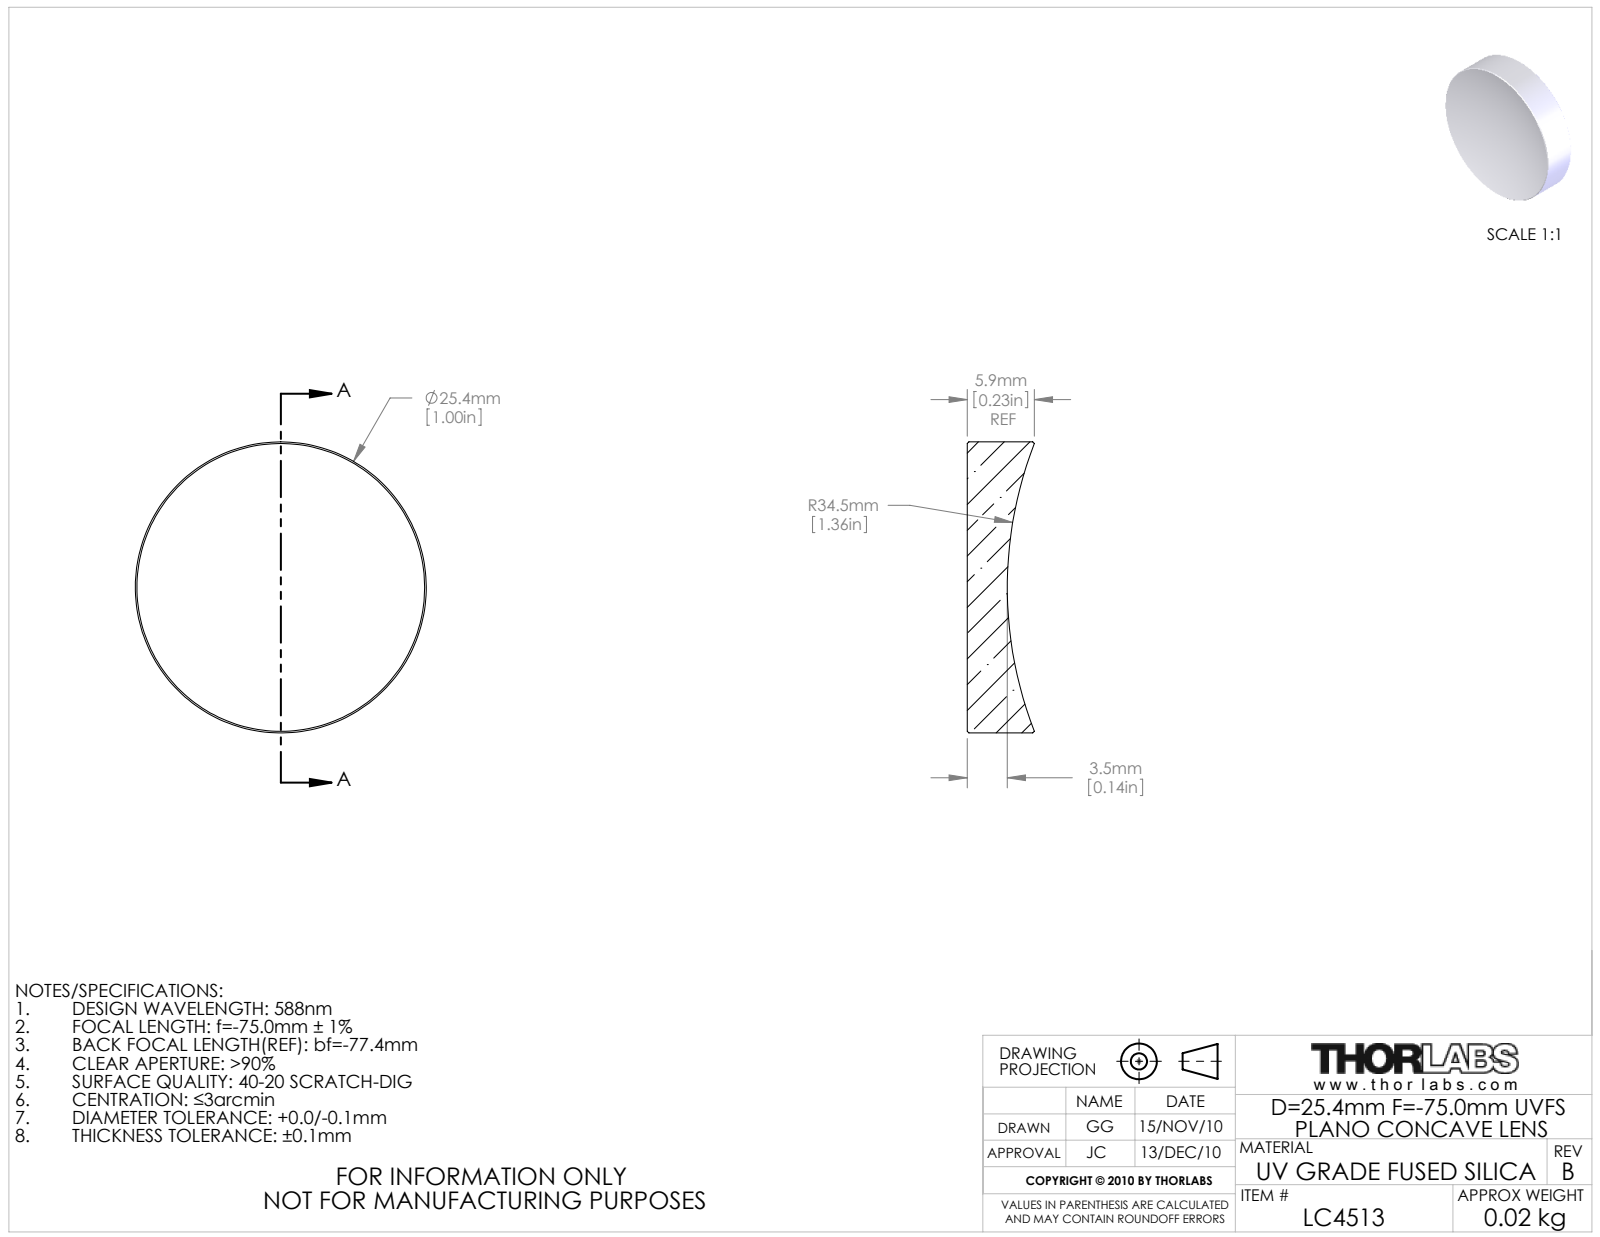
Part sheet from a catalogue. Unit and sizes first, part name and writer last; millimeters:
Units: millimetres
Overall size (bounding box): 25.4 × 25.4 × 5.87
Round bosses / shafts (diameter × count): ⌀25.4 ×1
Volume: 2 378 mm³ · Surface area: 1 486 mm²
Bodies: 1 solid, 9 faces (1 planar, 2 cylindrical, 6 other)
Part name (STEP PRODUCT): 3503-E0W
STEP written by: SolidWorks 2009 (AUTOMOTIVE_DESIGN)
